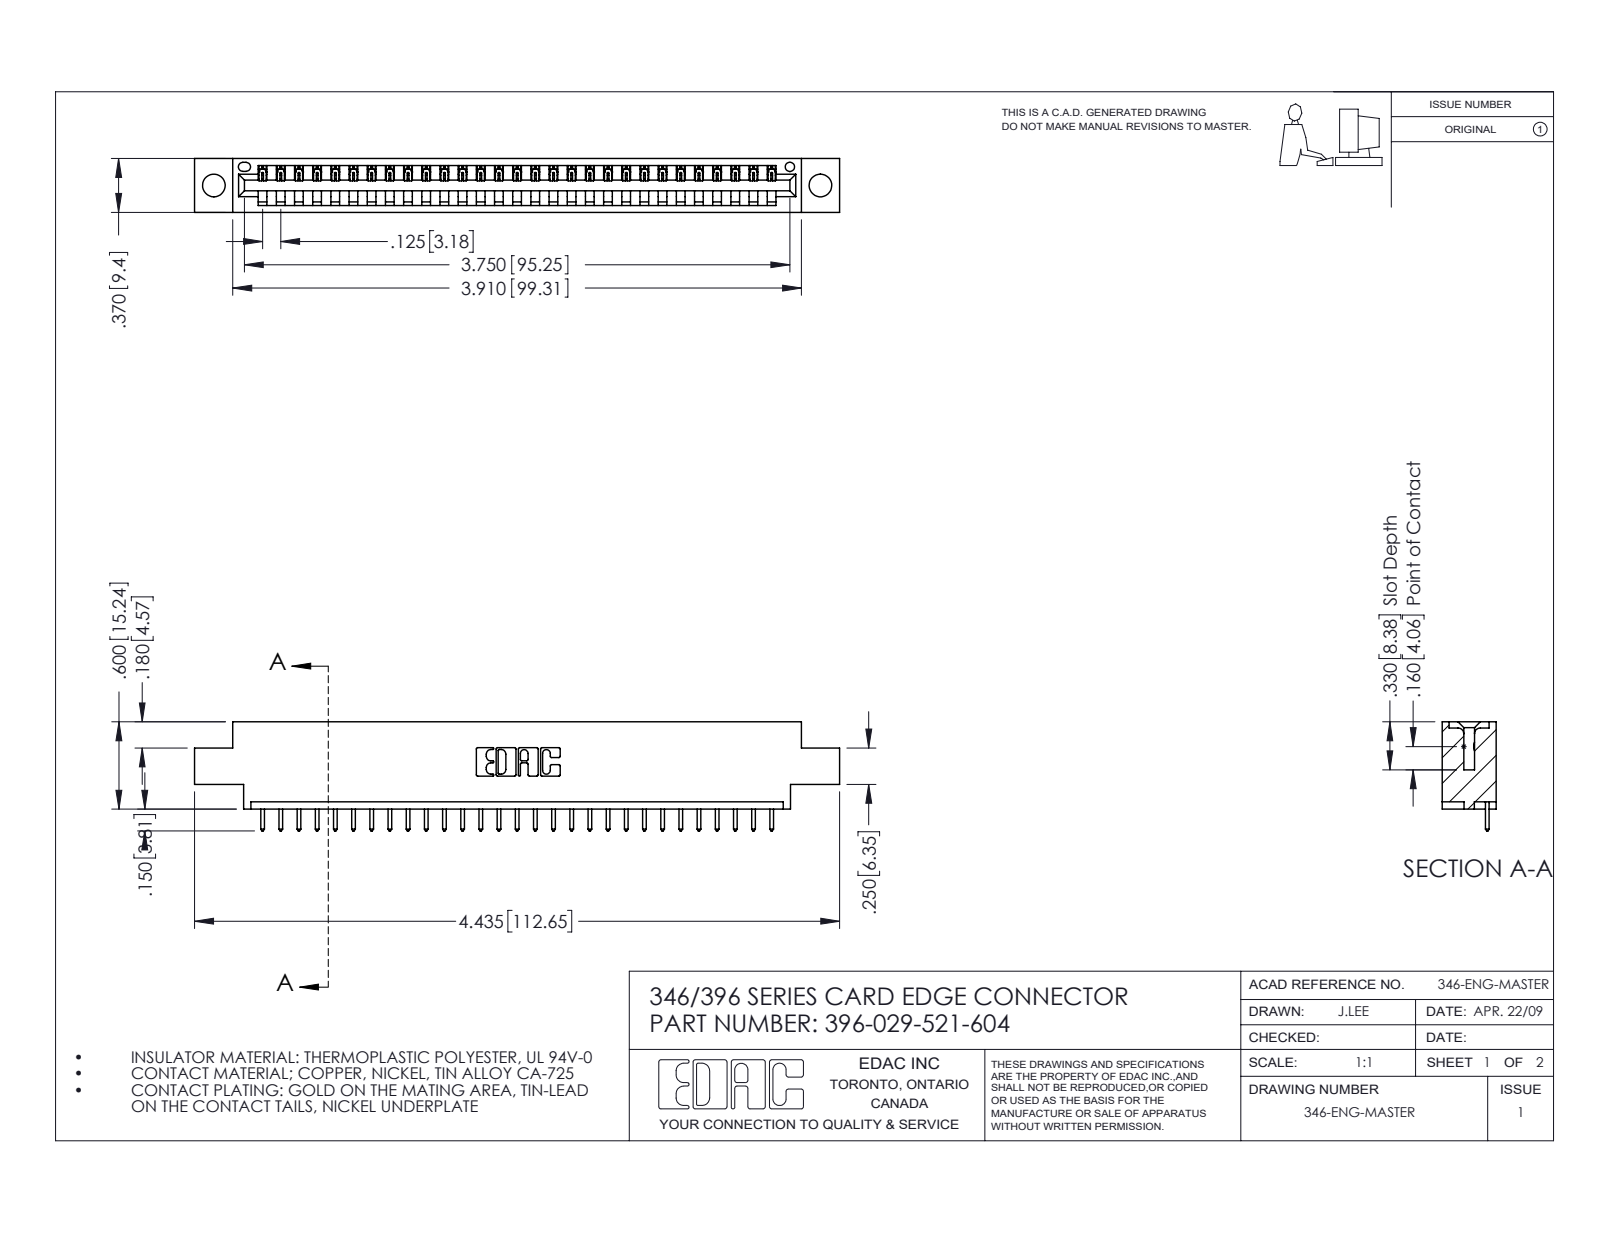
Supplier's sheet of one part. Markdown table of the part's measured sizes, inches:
| quantity | value |
| --- | --- |
| part name | 346 Part_0.170 Offset - 0.156 Dia-TH; 345-292-001_345-293-121; 396-029-521-604 |
| STEP written by | SolidWorks 2016 (CONFIG_CONTROL_DESIGN) |
| units | inches |
| bodies | 30 solids, 1808 faces (1240 planar, 568 cylindrical, 0 other) |
| overall size | 4.435 × 0.75 × 0.37 |
| volume | 0.633 in³ |
| surface area | 19.31 in² |
| round holes (diameter × count) | 0.156 × 2, 0.064 × 1 |
| partial cylindrical surfaces (radius × count) | 0.006 × 58, 0.01 × 58, 0.01 × 22, 0.007 × 6, 0.031 × 6, 0.026 × 3, 0.031 × 2, 0.04 × 2 |
| main face-to-face distances | 0.048, 0.322, 0.37, 0.25, 0.072, 0.298, 0.025, 0.148, 0.222, 0.1 |
| hole center spacings | 0.246, 3.962, 4.17 |
